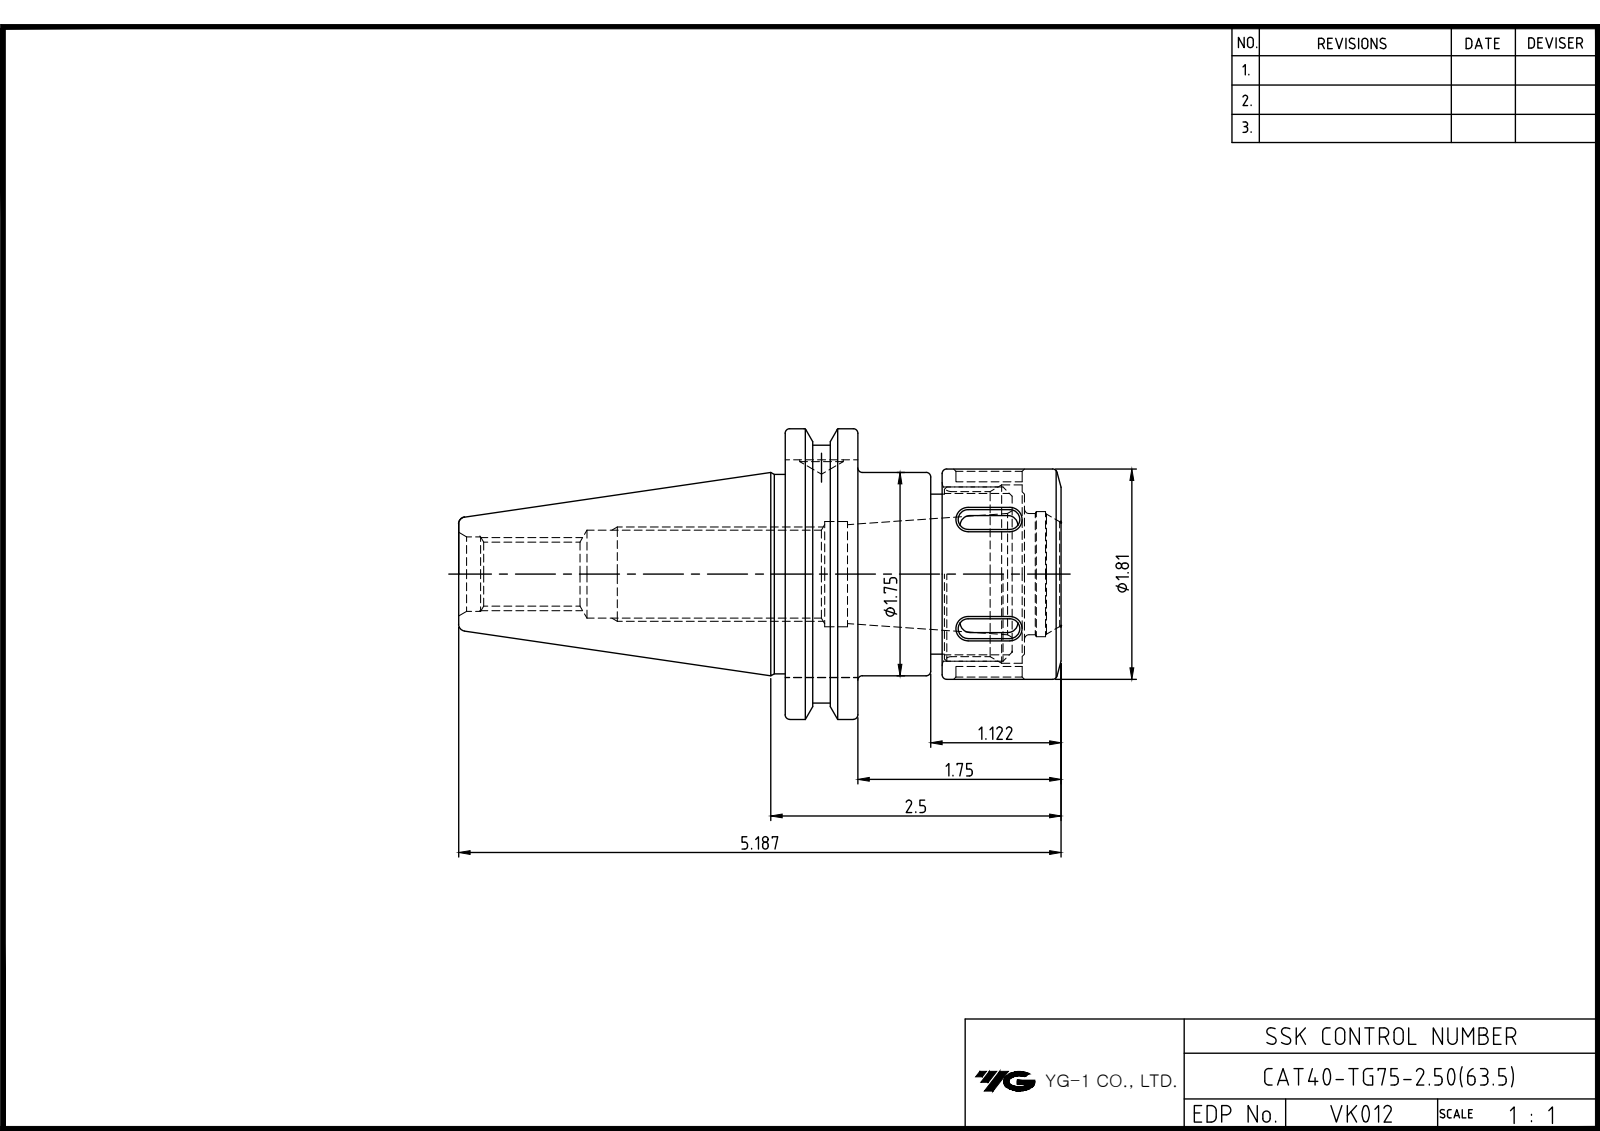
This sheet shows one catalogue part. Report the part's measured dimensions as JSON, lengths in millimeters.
{"part_name": "LO-CAT40-TG75-63.5; TG75 NUT", "step_written_by": "Autodesk Inventor 2025 (AP242_MANAGED_MODEL_BASED_3D_ENGINEERING_MIM_LF)", "units": "millimeters", "bodies": {"solids": 2, "faces": 73, "planar": 34, "cylindrical": 18, "other": 21}, "overall_size": [131.75, 63.5, 61.09], "volume_mm3": 136904, "surface_area_mm2": 36123, "round_holes": [[9.53, 1], [13.39, 1], [16.3, 1], [18.92, 1], [23, 1], [31.5, 1], [38.1, 1]], "round_bosses_or_shafts": [[63.5, 1], [56.3, 1], [46, 1], [44.45, 1], [43.6, 1], [35, 1]], "face_to_face_distances": [15.88, 60.33, 44.45, 31.83, 15.95, 28.5, 34.33, 18.45, 2.5, 26]}
